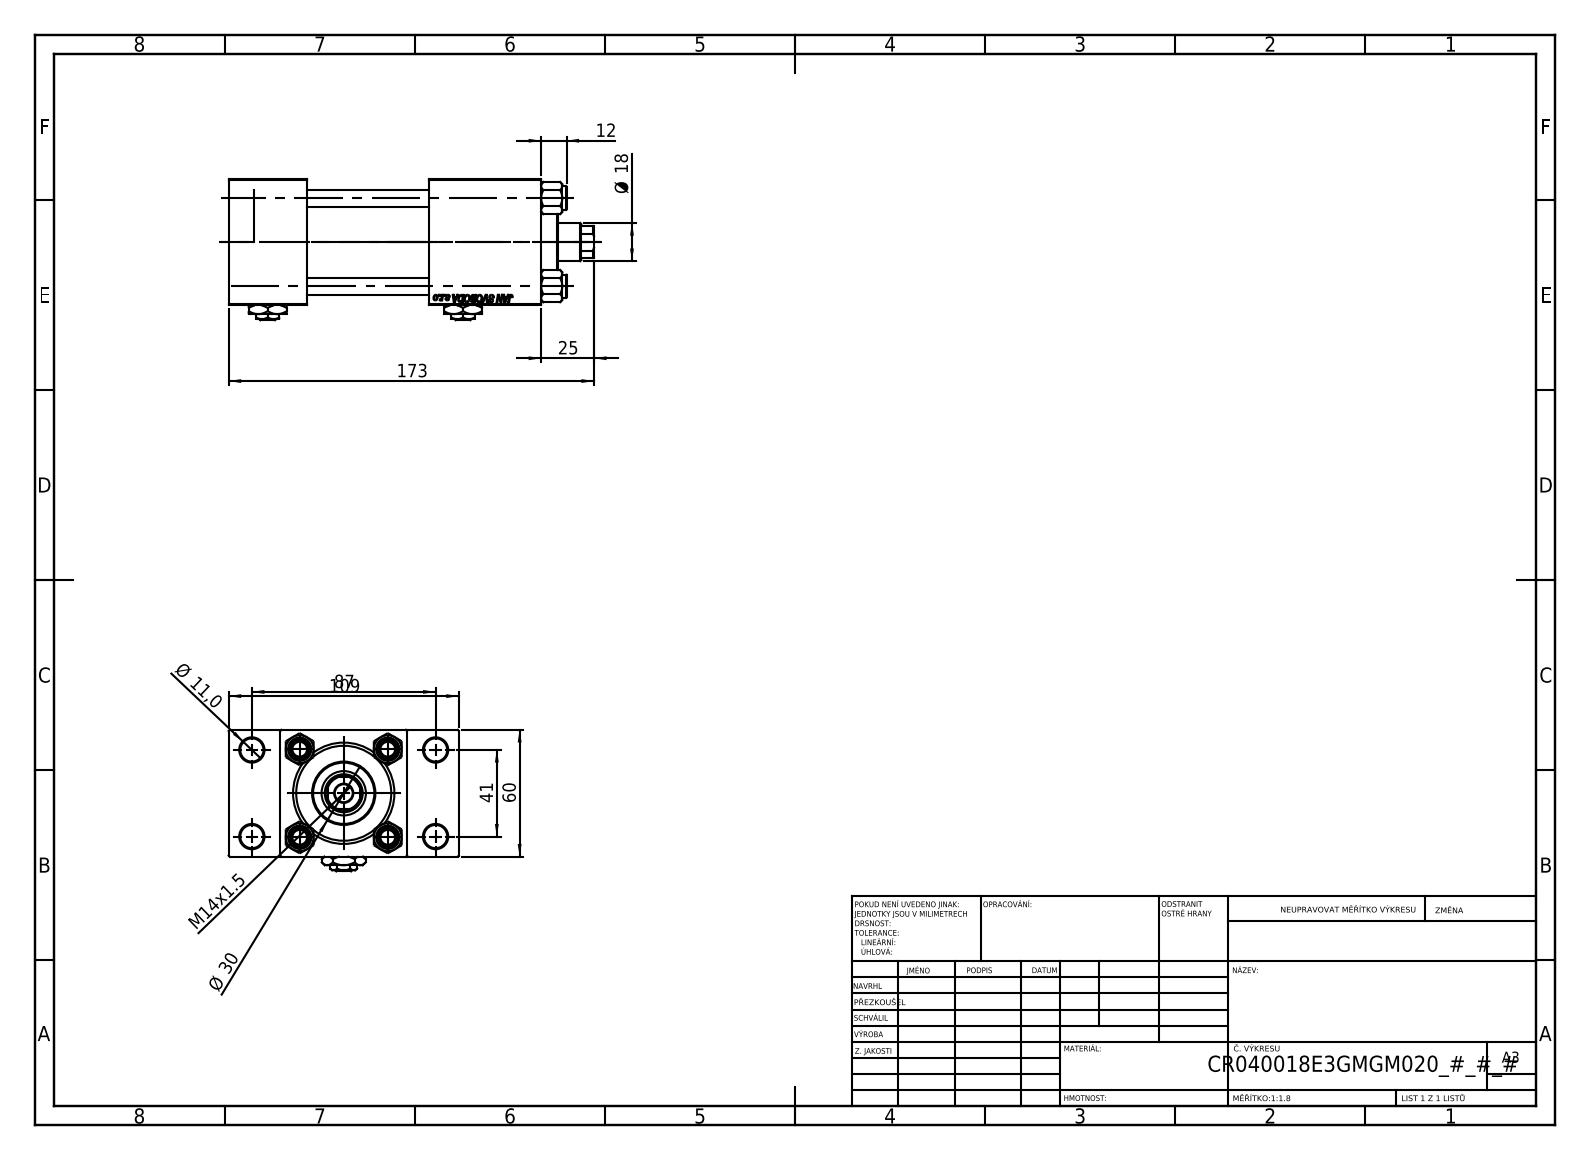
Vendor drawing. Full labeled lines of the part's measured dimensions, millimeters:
Part name (STEP PRODUCT): V215CR_TYCINKA_E; V215CR_VCP_E; NUT_M5_E; V215_VC_A (+2 more)
STEP written by: SolidWorks 2019 (CONFIG_CONTROL_DESIGN)
Units: millimetres
Bodies: 13 solids, 1237 faces (546 planar, 97 cylindrical, 594 other)
Overall size (bounding box): 173 × 109 × 67
Volume: 496 205 mm³ · Surface area: 127 374 mm²
Round holes (diameter × count): ⌀8 ×4, ⌀11 ×4, ⌀16.66 ×4, ⌀24 ×4, ⌀7 ×3, ⌀8.5 ×1, ⌀18 ×1, ⌀21 ×1, ⌀31 ×1, ⌀40 ×1, ⌀45 ×1
Round bosses / shafts (diameter × count): ⌀11 ×4, ⌀46 ×1, ⌀30 ×1
Partial cylindrical surfaces — rounded edges, fillets, slot ends (radius × count): R8.5 ×1
Main face-to-face distances: 60, 37, 24.5, 84.5, 148, 111, 24.3, 58, 53, 82.3
Hole centre spacings: 22.65, 29.49, 41.7, 47.15, 48.09, 64.35, 76.49, 41
